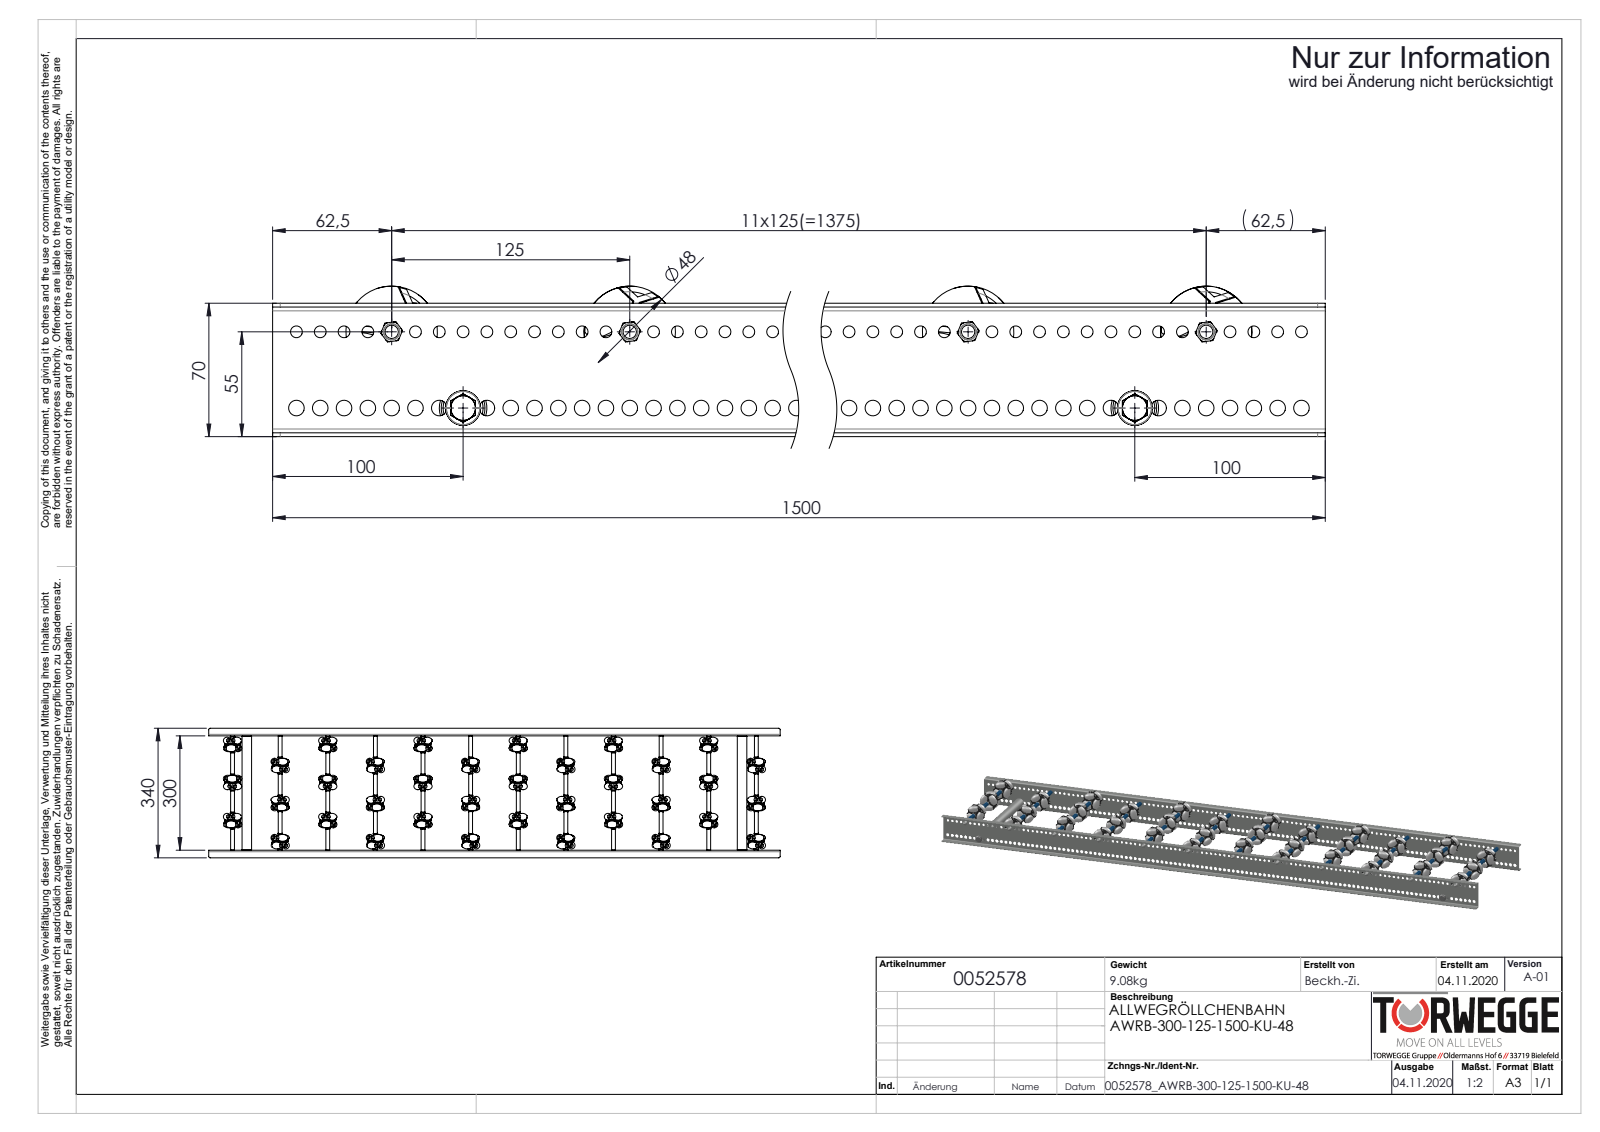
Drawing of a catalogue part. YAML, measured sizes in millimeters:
part_name: "0019719_Gewindestange-M6_L=320; AWR48_Röllchen; 0015028_AWR48; AWR48_Stift (+8 more)"
step_written_by: "SolidWorks 2020 (AUTOMOTIVE_DESIGN)"
units: millimeters
bodies: {solids: 624, faces: 11816, planar: 3864, cylindrical: 4872, other: 3080}
overall_size: [1500, 340, 79]
volume: 2434000
surface_area: 1811000
round_holes:
  - {diameter: 3.7, count: 216}
  - {diameter: 4.2, count: 216}
  - {diameter: 6.2, count: 119}
  - {diameter: 8.2, count: 119}
  - {diameter: 4.92, count: 12}
  - {diameter: 6.5, count: 12}
  - {diameter: 8.4, count: 12}
  - {diameter: 6.8, count: 2}
  - {diameter: 21, count: 2}
round_bosses_or_shafts:
  - {diameter: 4, count: 216}
  - {diameter: 3.7, count: 196}
  - {diameter: 8, count: 14}
  - {diameter: 42, count: 12}
  - {diameter: 11, count: 12}
  - {diameter: 10, count: 12}
  - {diameter: 7, count: 12}
  - {diameter: 6, count: 12}
partial_cylinders:
  - {radius: 23.55, count: 12}
  - {radius: 4, count: 8}
  - {radius: 2, count: 4}
face_to_face_distances: [2, 302, 68, 300, 304, 70, 66, 3, 20, 18]
hole_center_spacings: [36.06, 36.05, 10, 55.27, 12.5, 239.64, 248.59, 422.67]
